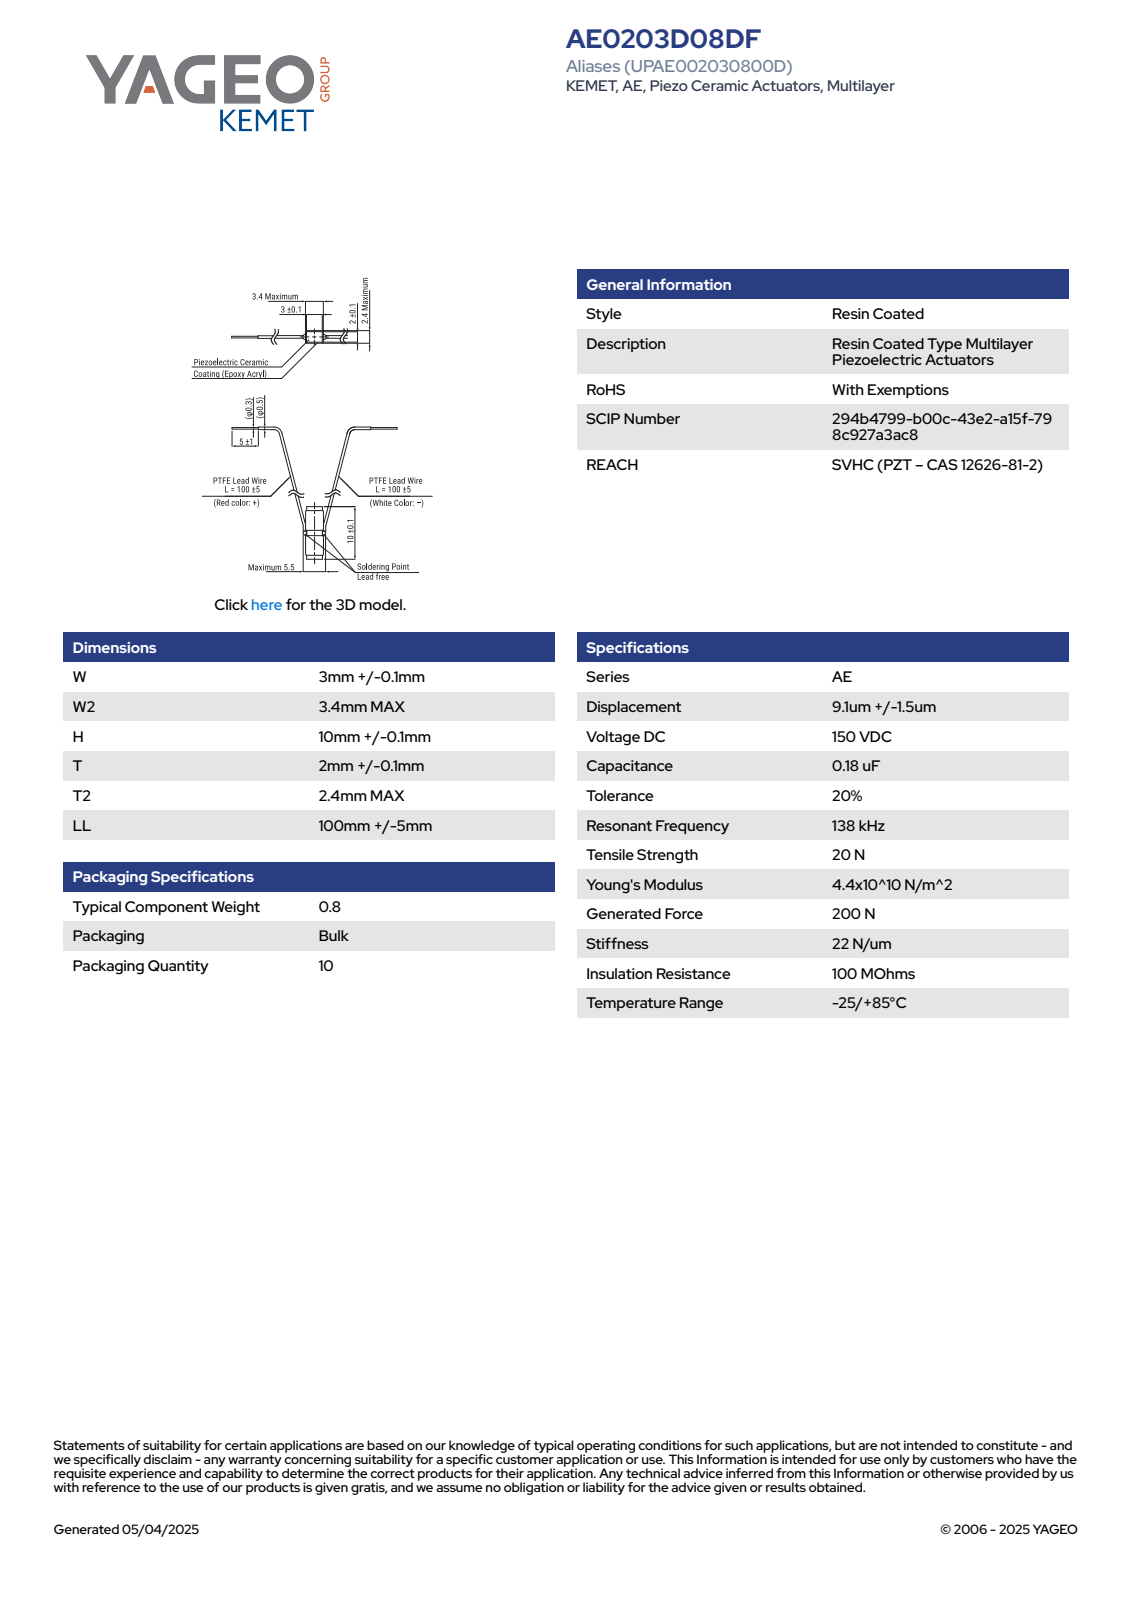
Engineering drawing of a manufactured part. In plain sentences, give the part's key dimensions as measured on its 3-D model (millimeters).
The part is named "AL_KAE1_W3.1W23.4H10.1T2.1T22.4". Its 3-D file was written by "SolidWorks 2014 (AUTOMOTIVE_DESIGN)". It is 4 solids with 93 faces: 85 planar, 8 cylindrical and 0 other. Overall it measures 10.11 by 3.4 by 2.4 millimeters. Its volume is 67 cubic millimeters and its surface area 127 square millimeters. Partial cylindrical surfaces (rounded edges, fillets, slot ends): 8 of radius 0.15. The main face-to-face distances are 2.25, 3, 2.1, 2.9, 2.4, 3.1, 10.1, 0.99, 4.06, 6.04.
